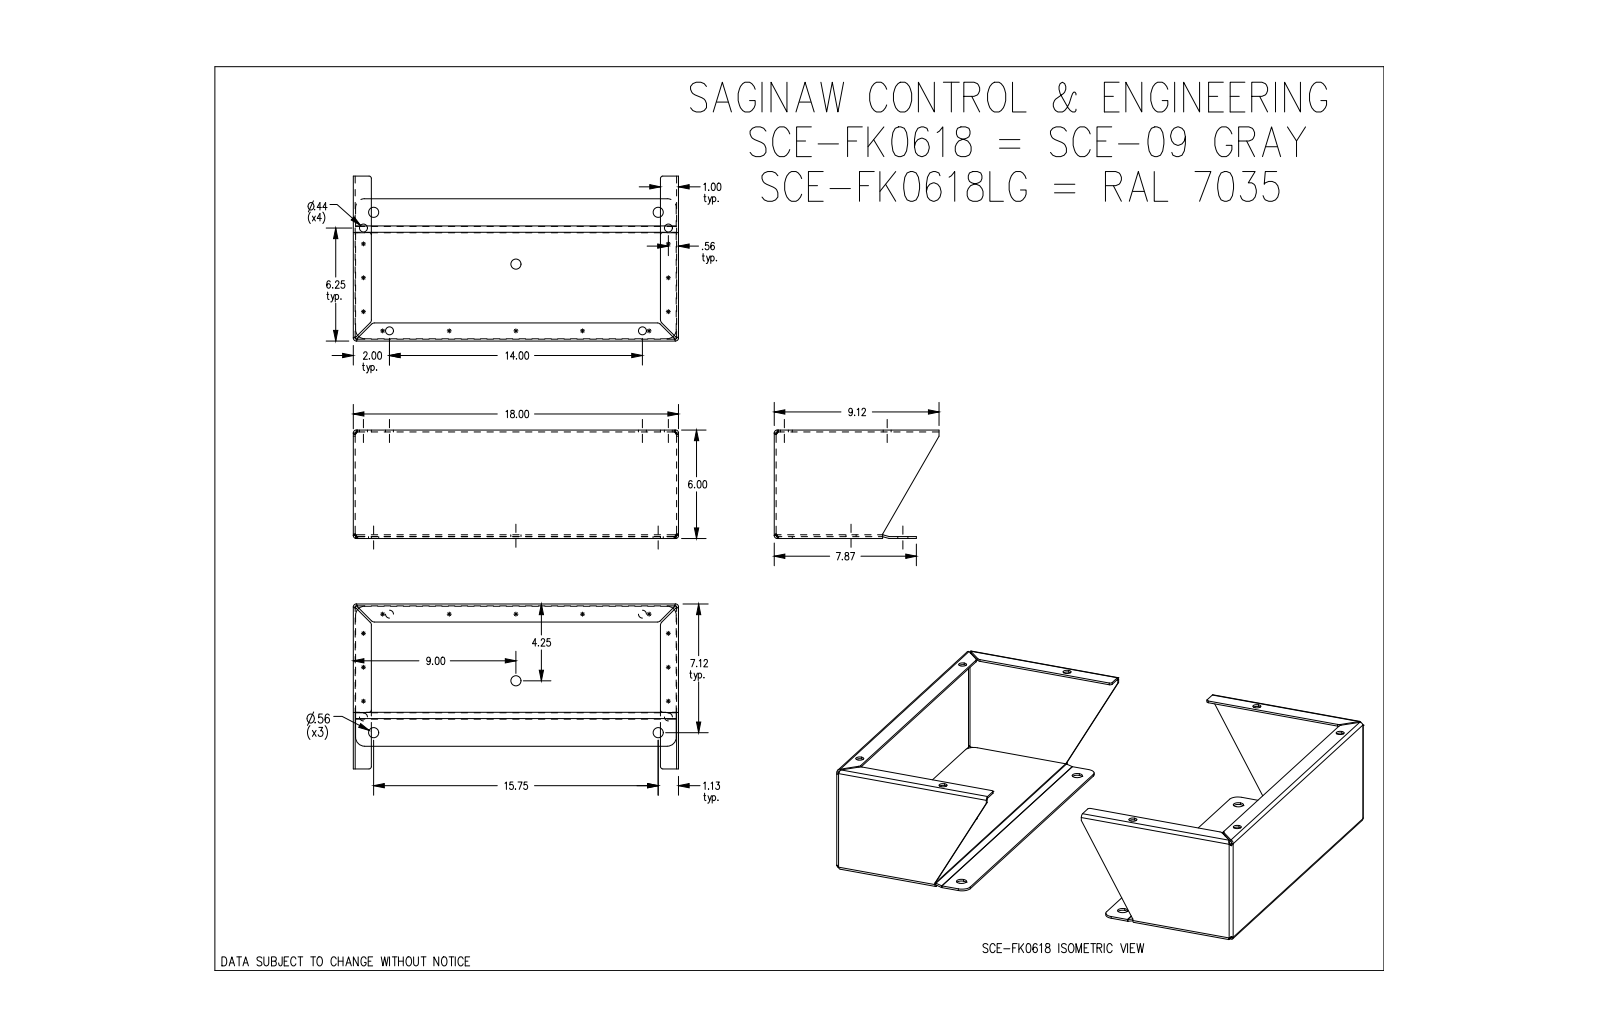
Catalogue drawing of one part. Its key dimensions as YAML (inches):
part_name: "SCE-FK0618"
step_written_by: "SolidWorks 2019 (CONFIG_CONTROL_DESIGN)"
units: inches
bodies: {solids: 4, faces: 214, planar: 96, cylindrical: 86, other: 32}
overall_size: [24, 18, 6]
volume: 80.03
surface_area: 1570
round_holes:
  - {diameter: 0.437, count: 8}
  - {diameter: 0.563, count: 6}
partial_cylinders:
  - {radius: 0.166, count: 16}
  - {radius: 0.062, count: 14}
  - {radius: 0.125, count: 8}
  - {radius: 0.22, count: 8}
  - {radius: 0.5, count: 8}
  - {radius: 0.063, count: 2}
face_to_face_distances: [0.104, 23.896, 17.896, 5.792, 0.101, 5.893, 5.896, 24, 23.792, 18]
hole_center_spacings: [1.035, 5.866, 6.614, 7.913, 8.671, 10.646, 14.884, 15.919]
